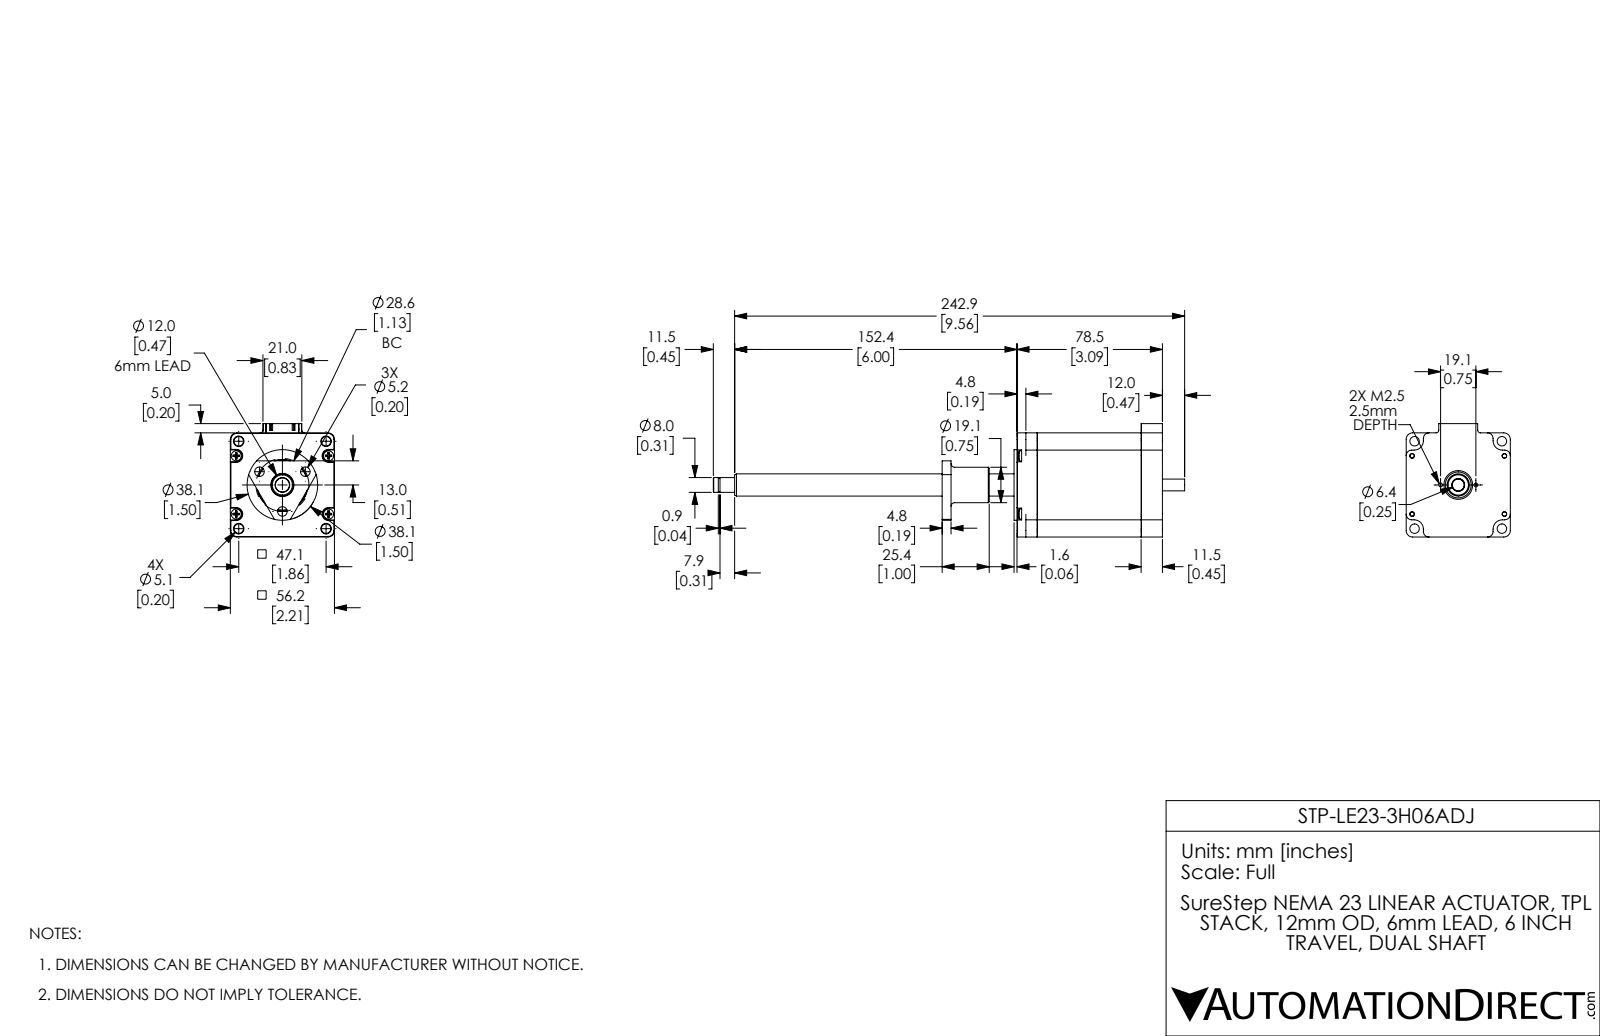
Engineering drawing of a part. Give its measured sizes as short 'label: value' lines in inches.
name: STP-LE23-3H06ADJ_2; STP-LE23-3H06ADJ_1; STP-LE23-3H06ADJ
written by: SolidWorks 2017 (AUTOMOTIVE_DESIGN)
unit: in
bodies: 7 solids, 1001 faces (380 planar, 460 cylindrical, 161 other)
size: 10.016 × 2.409 × 2.213
volume: 13.78 in³; area: 97.78 in²
holes: 8× ⌀0.177, 4× ⌀0.098, 4× ⌀0.13, 4× ⌀0.201, 3× ⌀0.203, 2× ⌀0.079, 2× ⌀0.081, 1× ⌀0.272, 1× ⌀0.413, 1× ⌀0.583, 1× ⌀0.61, 1× ⌀0.63
bosses: 4× ⌀0.213, 4× ⌀0.115, 1× ⌀1.5, 1× ⌀1.417, 1× ⌀1.402, 1× ⌀1.372, 1× ⌀1.102, 1× ⌀0.752
rounds: 10× R0.059, 8× R0.008, 8× R0.118, 4× R0.071, 4× R0.126, 4× R0.138, 4× R0.197, 1× R0.024
face distances: 2.213, 2.205, 0.453, 2.657, 3.091, 0.433, 2.024, 2.638, 0.063, 0.043
hole spacings: 0.974, 0.556, 1.301, 1.378, 1.801, 1.911, 2.244, 0.258
